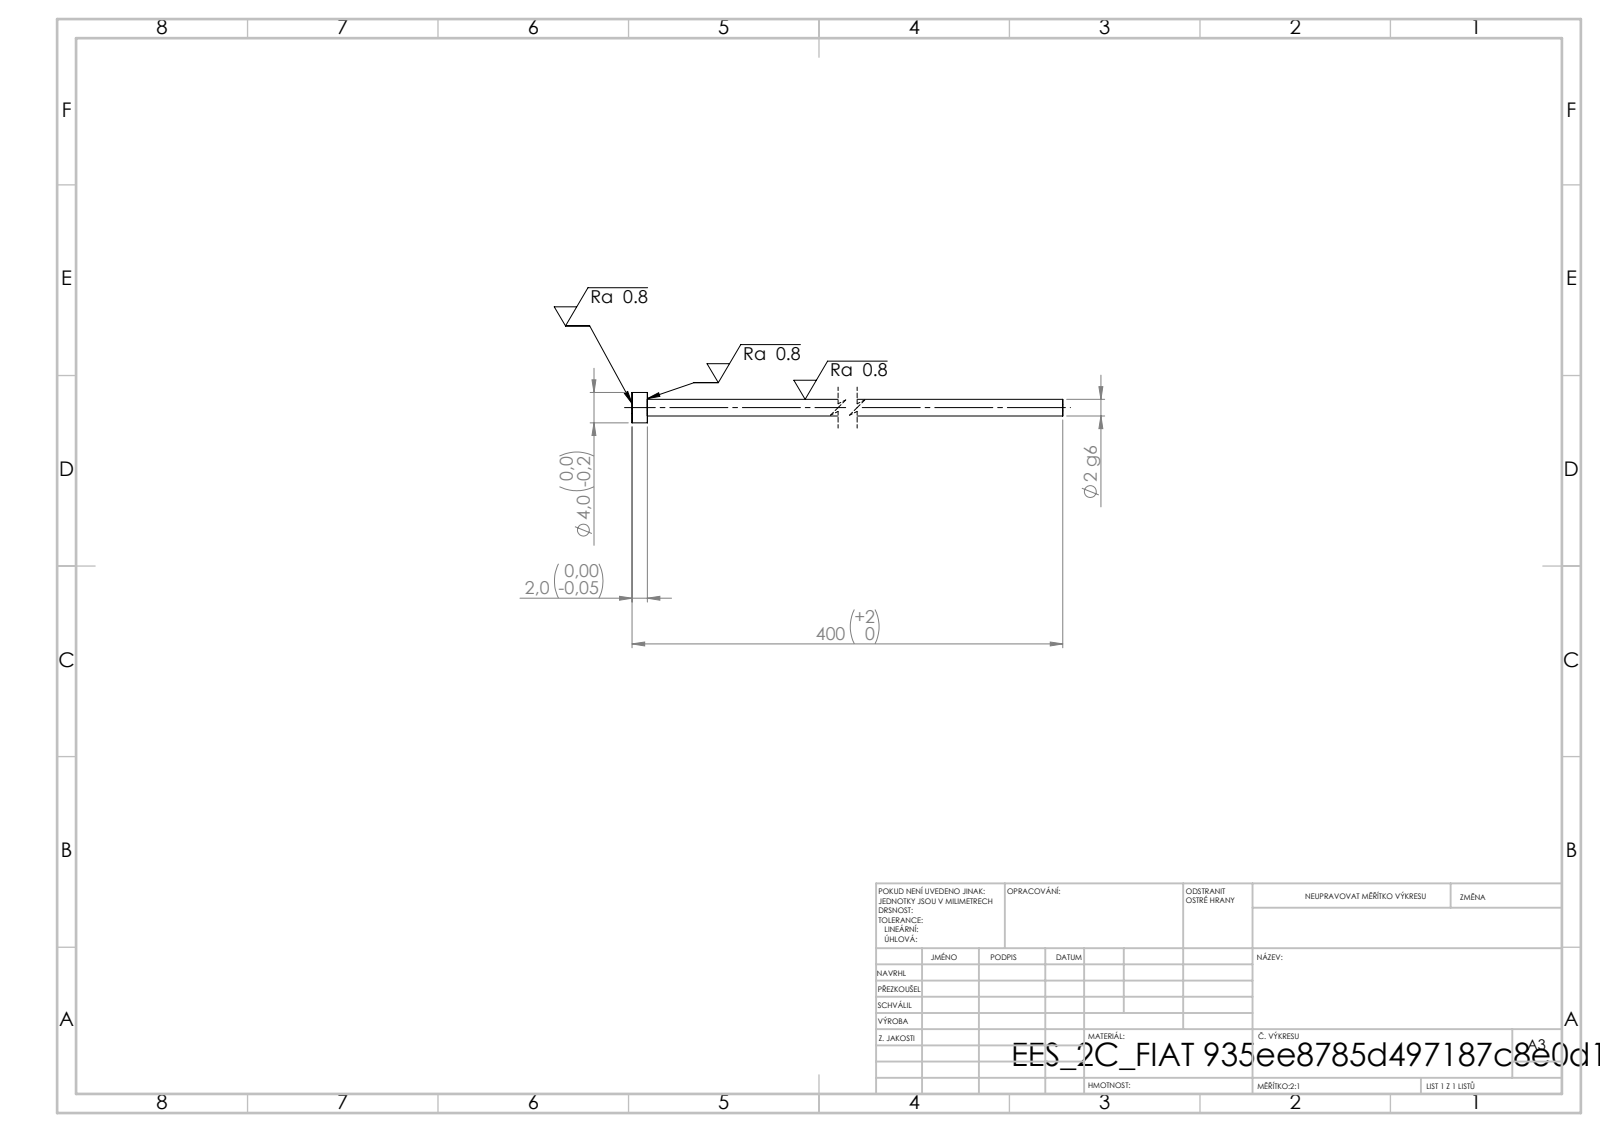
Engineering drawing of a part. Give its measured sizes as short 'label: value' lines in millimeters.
written by: SolidWorks 2019 (CONFIG_CONTROL_DESIGN)
unit: mm
bodies: 1 solid, 7 faces (3 planar, 4 cylindrical, 0 other)
size: 400 × 4 × 4
volume: 1 538 mm³; area: 2 801 mm²
bosses: 1× ⌀4, 1× ⌀2.2
face distances: 2, 400, 398
